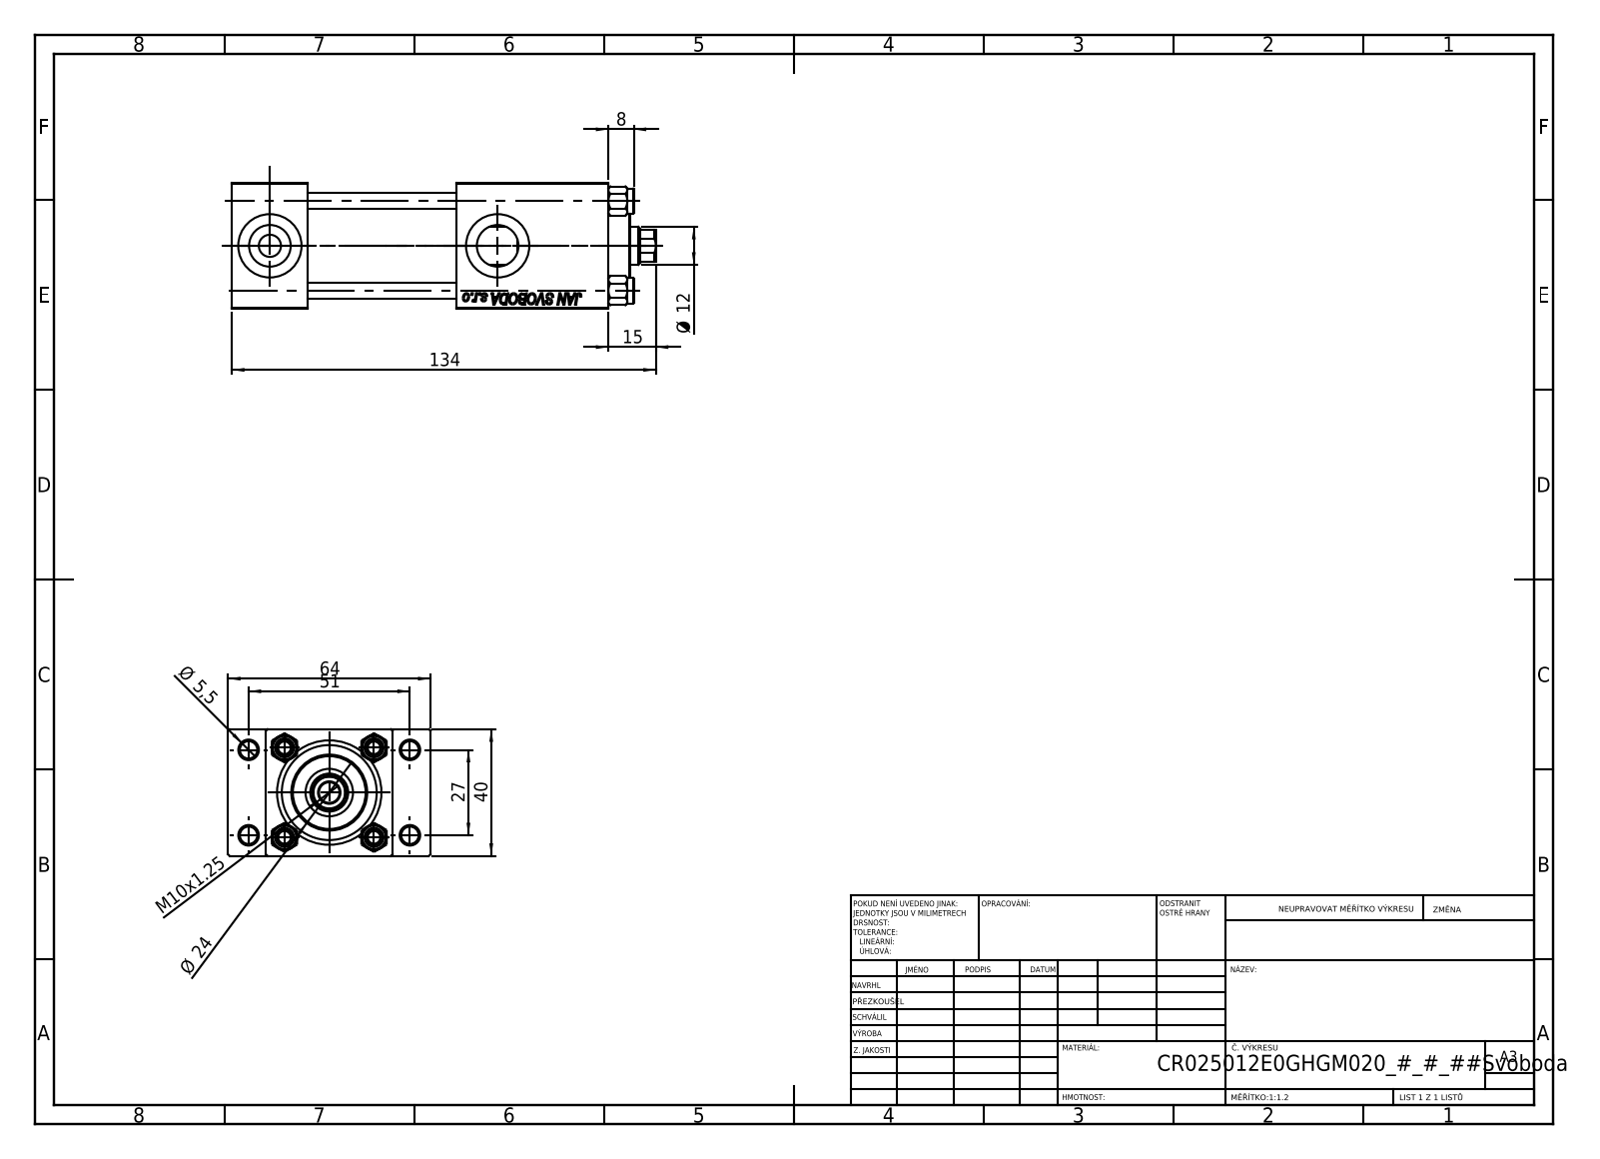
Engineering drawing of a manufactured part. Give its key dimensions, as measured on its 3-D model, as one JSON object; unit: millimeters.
{"part_name": "V215CR_VCP_E; V215CR_TYCINKA_E; V215_VC_A; NUT_M5_E (+1 more)", "step_written_by": "SolidWorks 2019 (CONFIG_CONTROL_DESIGN)", "units": "millimeters", "bodies": {"solids": 11, "faces": 1135, "planar": 497, "cylindrical": 86, "other": 552}, "overall_size": [134, 64, 40], "volume_mm3": 163534, "surface_area_mm2": 62368, "round_holes": [[5, 4], [5.5, 4], [20, 3], [7, 2], [13.16, 2], [6.5, 1], [12, 1], [15, 1], [25, 1], [30, 1]], "round_bosses_or_shafts": [[8, 4], [31, 1], [24, 1]], "partial_cylinders_radius": [[5.5, 1]], "face_to_face_distances": [40, 24, 12, 52, 119, 95, 90.3, 66.3, 28.7, 47], "hole_center_spacings": [11.37, 20.01, 28.3, 28.85, 29.89, 39.66, 48.34, 27]}
